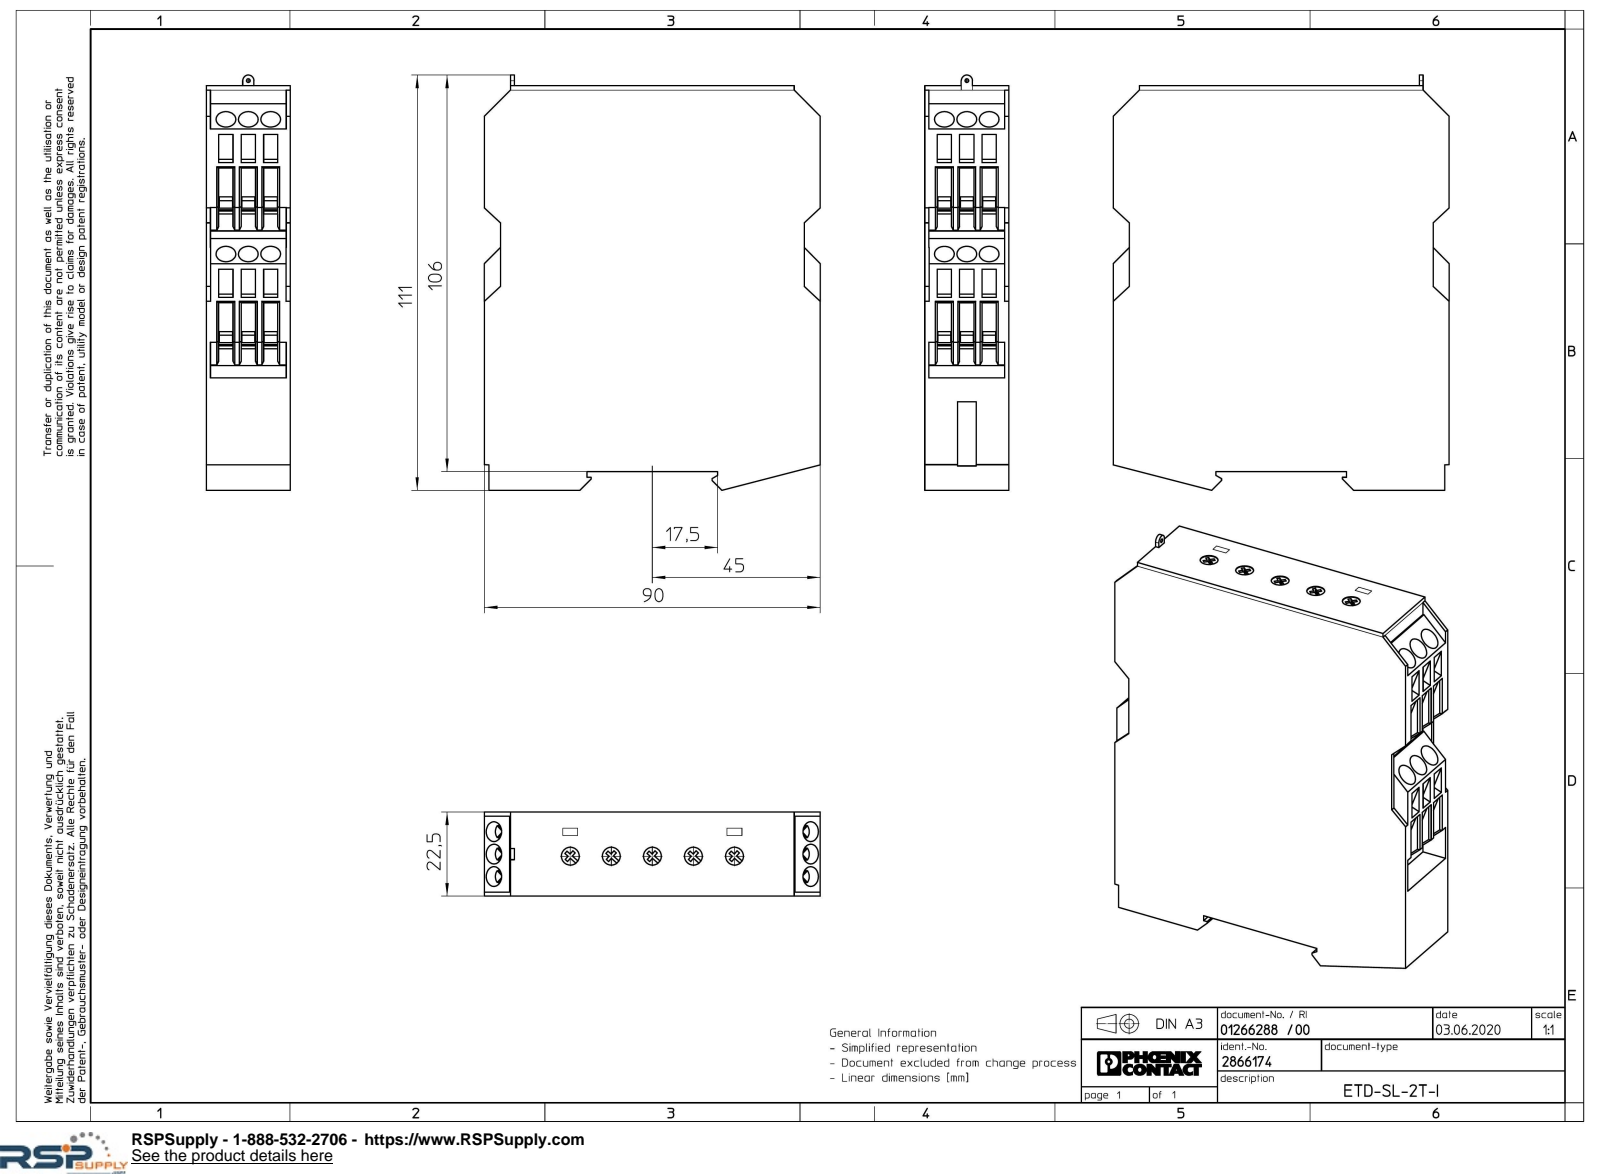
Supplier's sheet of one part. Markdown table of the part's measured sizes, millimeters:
| quantity | value |
| --- | --- |
| part name | ETD-SL-2T-I-select |
| STEP written by | Creo Elements/Direct Modeling 20.1A 29-Sep-2018 (C) Parametric Technology GmbH (AUTOMOTIVE_DESIGN) |
| units | millimeters |
| bodies | 1 solid, 665 faces (598 planar, 37 cylindrical, 30 other) |
| overall size | 111 × 90 × 22.5 |
| volume | 198 325 mm³ |
| surface area | 33 780 mm² |
| round holes (diameter × count) | 5.3 × 12, 4.8 × 5, 1 × 1 |
| partial cylindrical surfaces (radius × count) | 1.5 × 1 |
| main face-to-face distances | 22.5, 6, 90, 12, 103.15, 3.8, 7, 3.5, 2.2, 3.65 |
| hole center spacings | 6, 12.31, 11, 12, 13.69, 13.7, 17.19, 22 |
